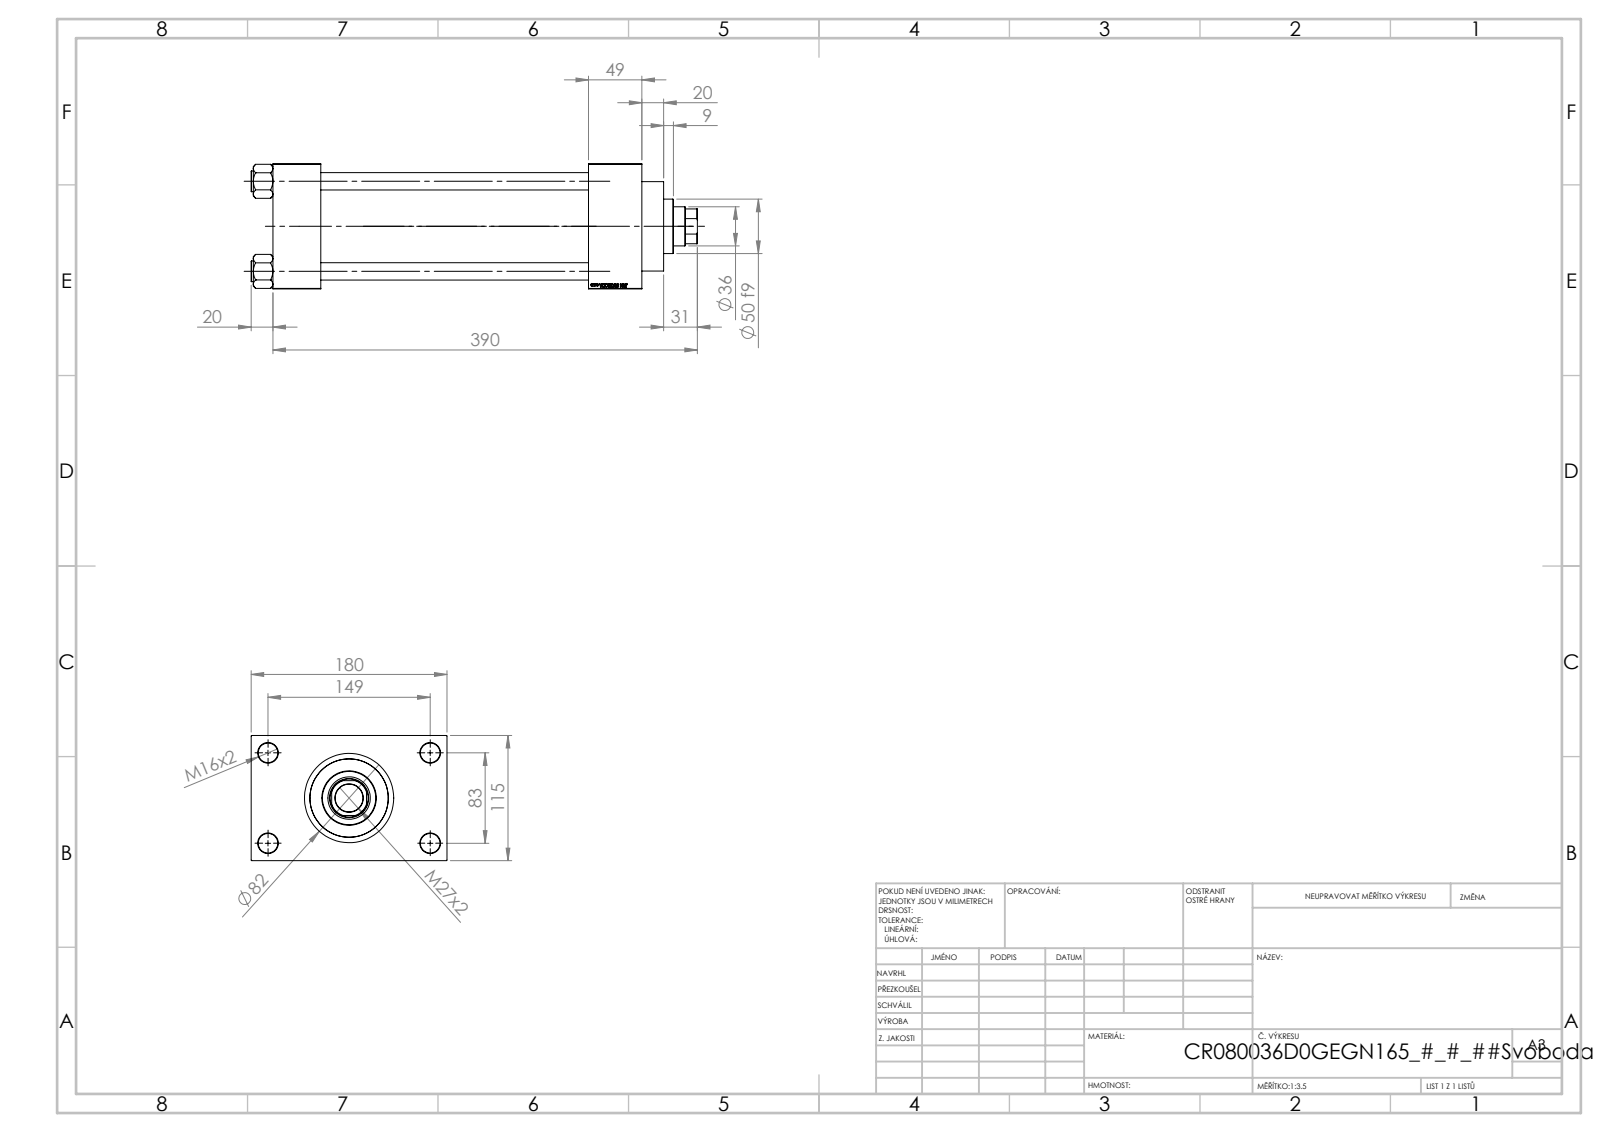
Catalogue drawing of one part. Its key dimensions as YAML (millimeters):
part_name: "V215CR_VCP_D; V215CR_D_Body; V215CR_D_TYCINKA; V215_VC_A (+1 more)"
step_written_by: "SolidWorks 2019 (CONFIG_CONTROL_DESIGN)"
units: millimeters
bodies: {solids: 11, faces: 1152, planar: 545, cylindrical: 89, other: 518}
overall_size: [410, 180, 115]
volume: 2466000
surface_area: 444317
round_holes:
  - {diameter: 16, count: 4}
  - {diameter: 18, count: 4}
  - {diameter: 7, count: 2}
  - {diameter: 26.44, count: 2}
  - {diameter: 35, count: 2}
  - {diameter: 25.5, count: 1}
  - {diameter: 36, count: 1}
  - {diameter: 39, count: 1}
  - {diameter: 61, count: 1}
  - {diameter: 72, count: 1}
  - {diameter: 80, count: 1}
round_bosses_or_shafts:
  - {diameter: 19, count: 4}
  - {diameter: 86, count: 1}
  - {diameter: 82, count: 1}
  - {diameter: 50, count: 1}
partial_cylinders:
  - {radius: 17.5, count: 1}
face_to_face_distances: [115, 246, 295, 49, 44, 290, 339, 32.5, 147.5, 180]
hole_center_spacings: [33.15, 58.48, 82.7, 85.28, 89.24, 115.85, 142.43, 83]
